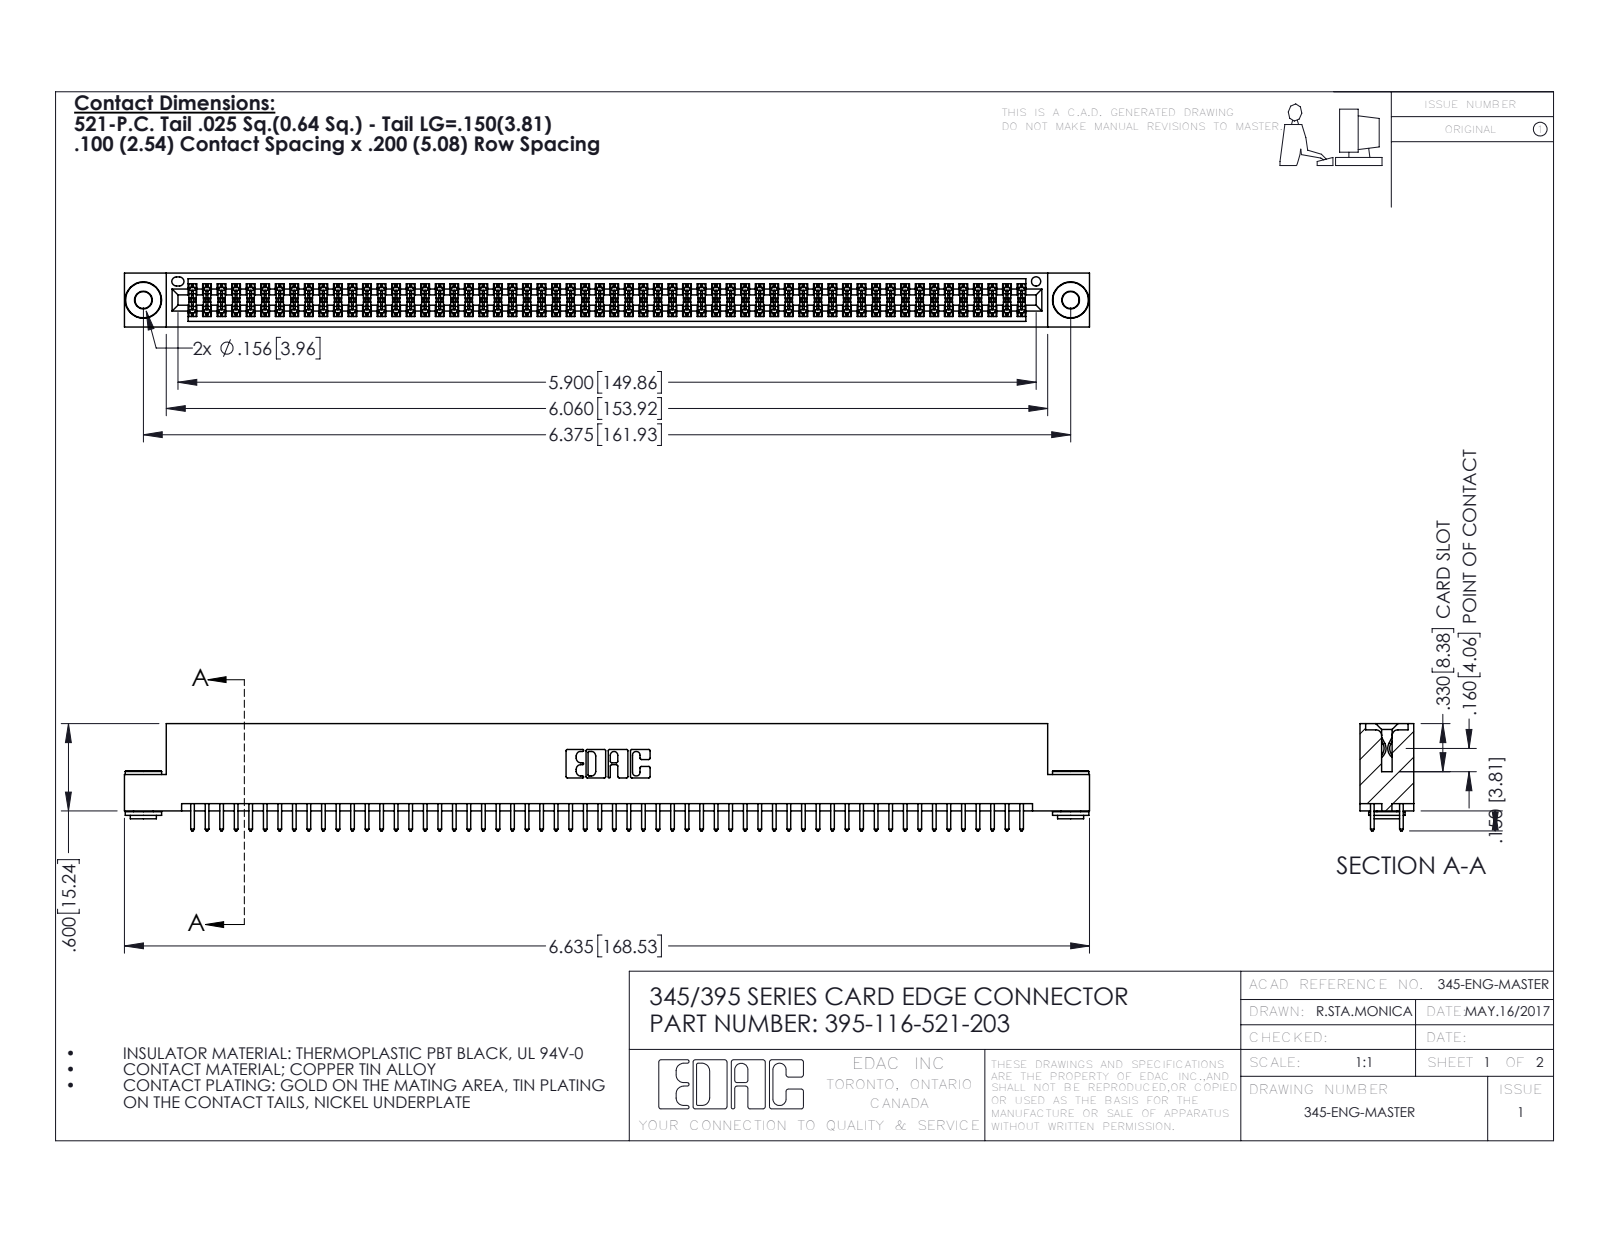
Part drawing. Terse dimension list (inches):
name: 345-292-001_345-293-121; 345-250-002_345-250-002-102; 395-116-521-203; 345 Part_Flush Mounting Lugs - 0.156 Dia-TH
written by: SolidWorks 2016 (CONFIG_CONTROL_DESIGN)
unit: in
bodies: 119 solids, 5964 faces (3918 planar, 2038 cylindrical, 8 other)
size: 6.635 × 0.737 × 0.37
volume: 1.006 in³; area: 38.11 in²
holes: 2× ⌀0.116, 2× ⌀0.156, 1× ⌀0.064
bosses: 2× ⌀0.25, 2× ⌀0.18, 2× ⌀0.136
rounds: 174× R0.006, 116× R0.01, 22× R0.01, 6× R0.007, 6× R0.031, 3× R0.026, 2× R0.014, 2× R0.019
face distances: 0.072, 0.298, 0.2, 0.025, 0.098, 0.272, 0.37, 0.225, 0.175, 0.149
hole spacings: 0.27, 6.139, 6.375
